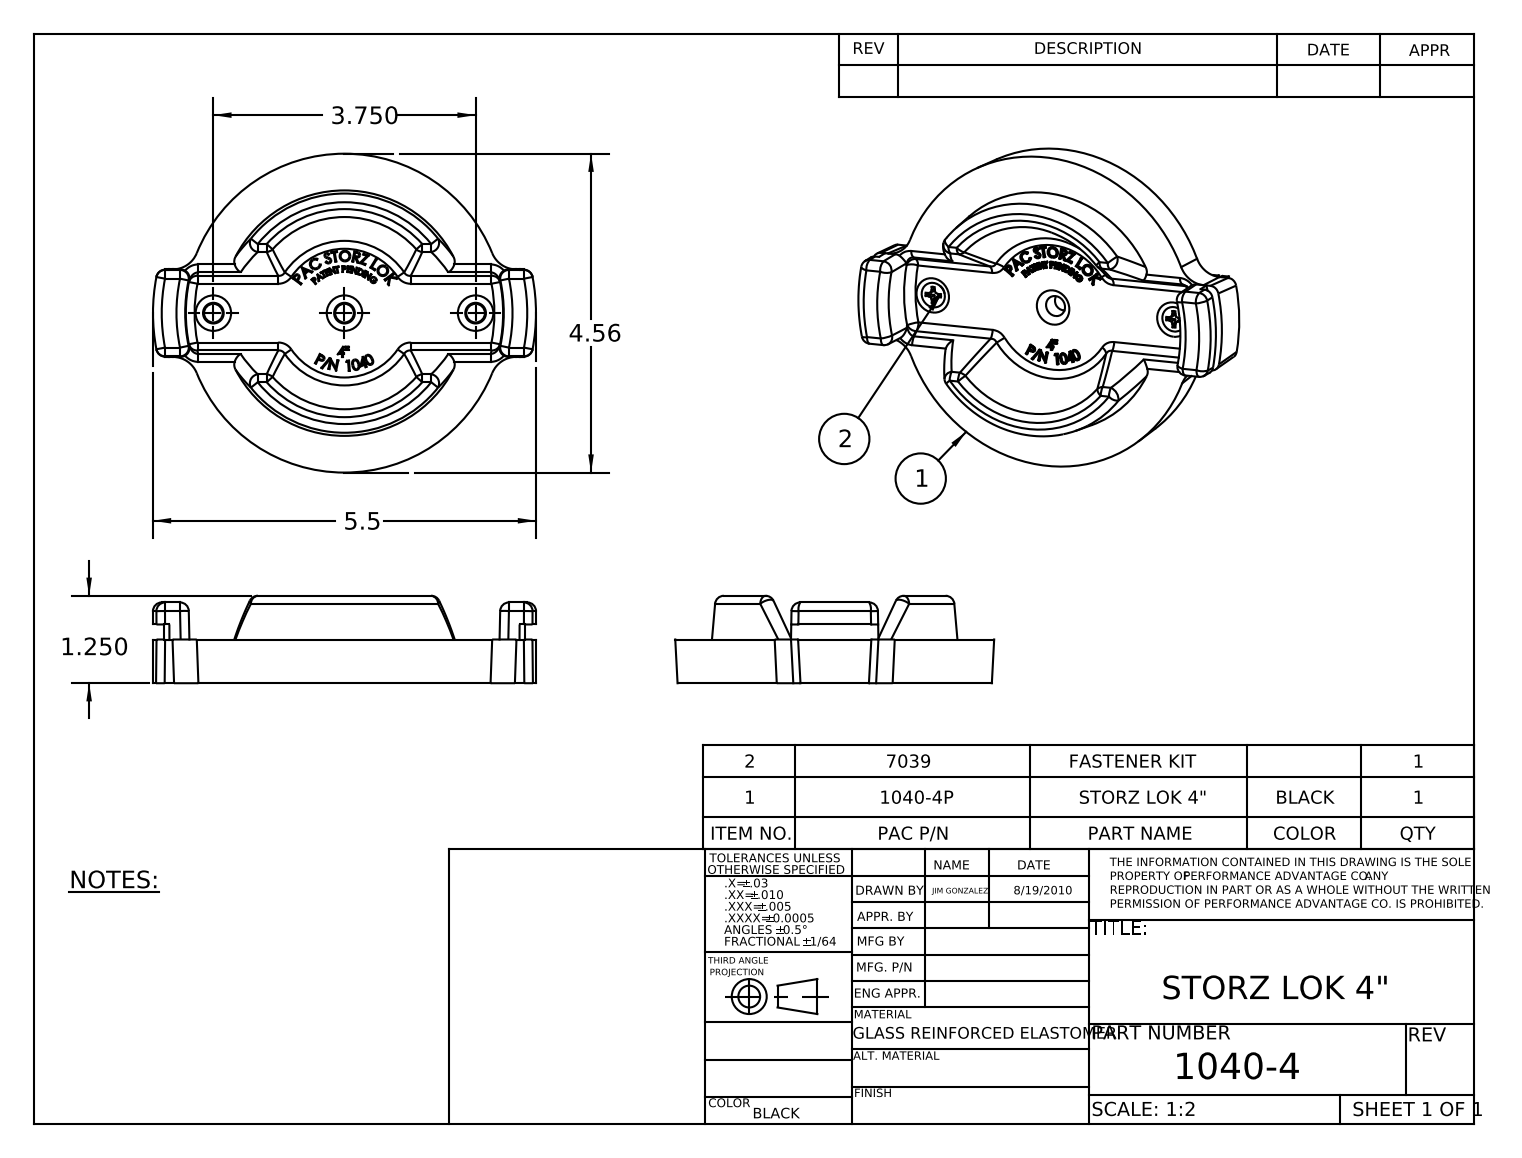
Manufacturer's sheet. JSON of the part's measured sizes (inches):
{"part_name": "1040-4", "step_written_by": "SolidWorks 2010 (CONFIG_CONTROL_DESIGN)", "units": "inches", "bodies": {"solids": 1, "faces": 595, "planar": 332, "cylindrical": 26, "other": 237}, "overall_size": [5.477, 4.56, 1.25], "volume_in3": 8.731, "surface_area_in2": 66.97, "partial_cylinders_radius": [[0.125, 8], [0.03, 4], [2.58, 1], [2.739, 1]], "face_to_face_distances": [0.25, 0.375, 0.625, 0.125, 0.5, 1.25, 1.125, 0.875, 0.625, 1.155]}
